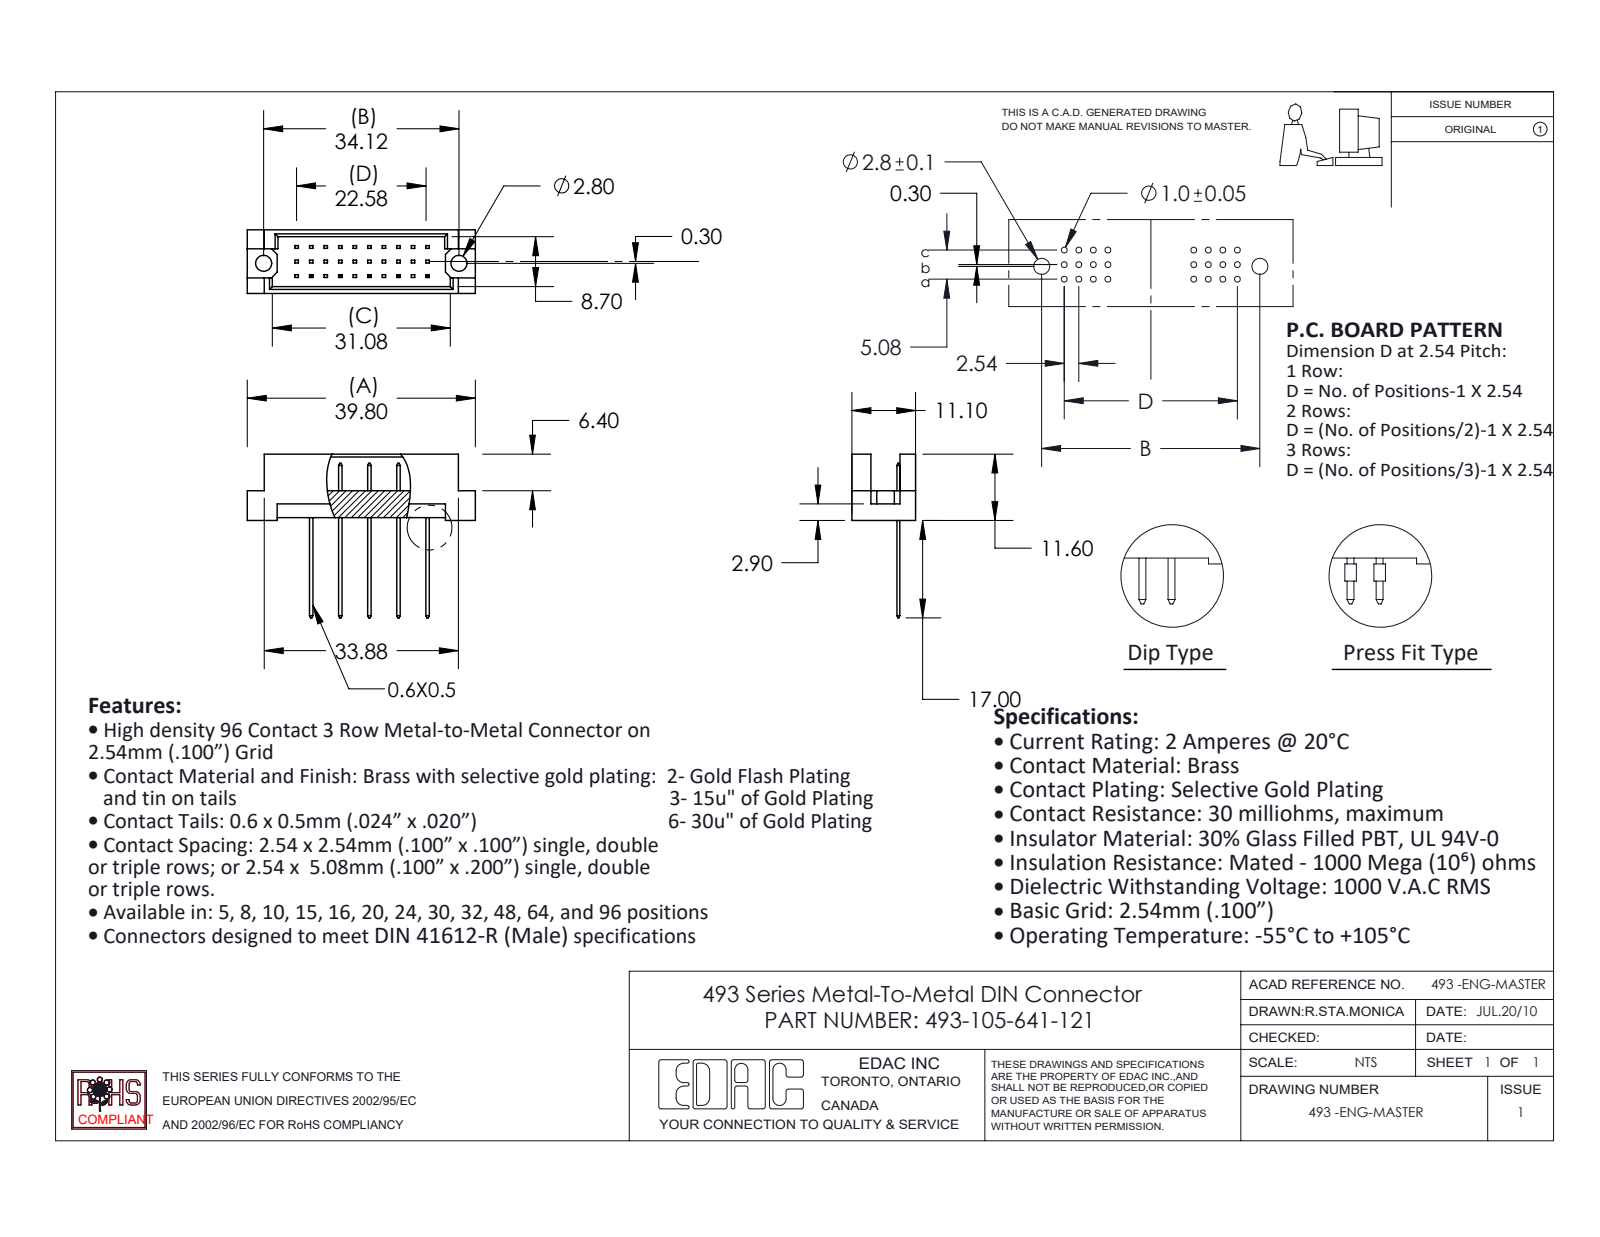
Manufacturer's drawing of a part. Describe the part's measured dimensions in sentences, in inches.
The part is named "493 Part_30; 493-290_41; 493-105-641-122". Its 3-D file was written by "SolidWorks 2020 (CONFIG_CONTROL_DESIGN)". It is 6 solids with 242 faces: 238 planar, 4 cylindrical and 0 other. Overall it measures 1.567 by 1.126 by 0.437 inches. Its volume is 0.147 cubic inches and its surface area 4.701 square inches. Round holes: 2 of diameter 0.11. The main face-to-face distances are 0.047, 0.39, 0.437, 0.343, 0.02, 0.2, 0.185, 0.109, 0.128, 0.309. The hole center spacings are 1.343.
